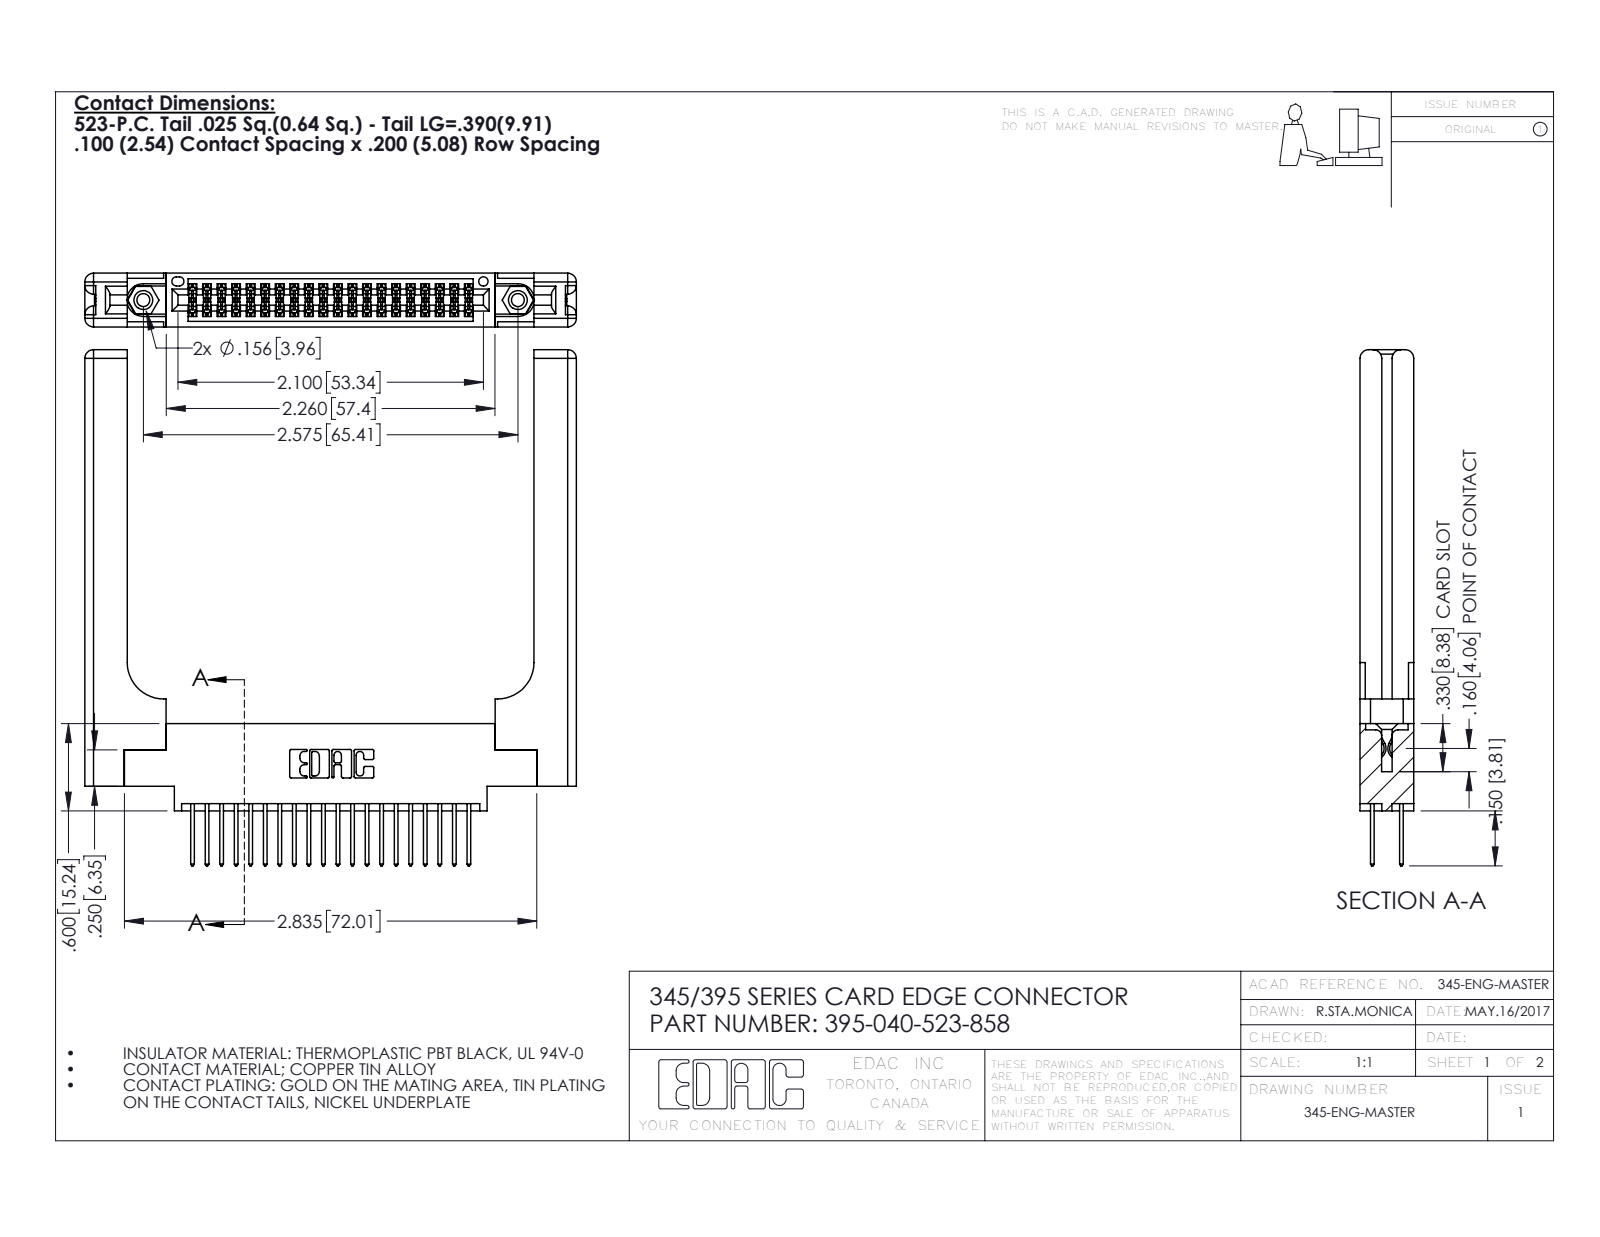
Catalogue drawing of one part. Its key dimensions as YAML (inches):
part_name: "345 Part_0.170 Offset - 0.156 Dia-TH; 345-250-001_345-250-001-102; 345-292-001_345-293-123; 345-220-058_345-220-058 (+1 more)"
step_written_by: "SolidWorks 2016 (CONFIG_CONTROL_DESIGN)"
units: inches
bodies: {solids: 45, faces: 2386, planar: 1552, cylindrical: 774, other: 60}
overall_size: [3.547, 3.379, 0.37]
volume: 1.012
surface_area: 26.54
round_holes:
  - {diameter: 0.089, count: 2}
  - {diameter: 0.125, count: 2}
  - {diameter: 0.156, count: 2}
  - {diameter: 0.064, count: 1}
round_bosses_or_shafts:
  - {diameter: 0.155, count: 2}
partial_cylinders:
  - {radius: 0.006, count: 60}
  - {radius: 0.01, count: 40}
  - {radius: 0.01, count: 22}
  - {radius: 0.06, count: 16}
  - {radius: 0.007, count: 6}
  - {radius: 0.031, count: 6}
  - {radius: 0.026, count: 3}
  - {radius: 0.014, count: 2}
face_to_face_distances: [0.37, 0.072, 0.298, 0.098, 0.272, 0.025, 0.2, 0.148, 0.15, 0.225]
hole_center_spacings: [0.27, 2.341, 2.575]
